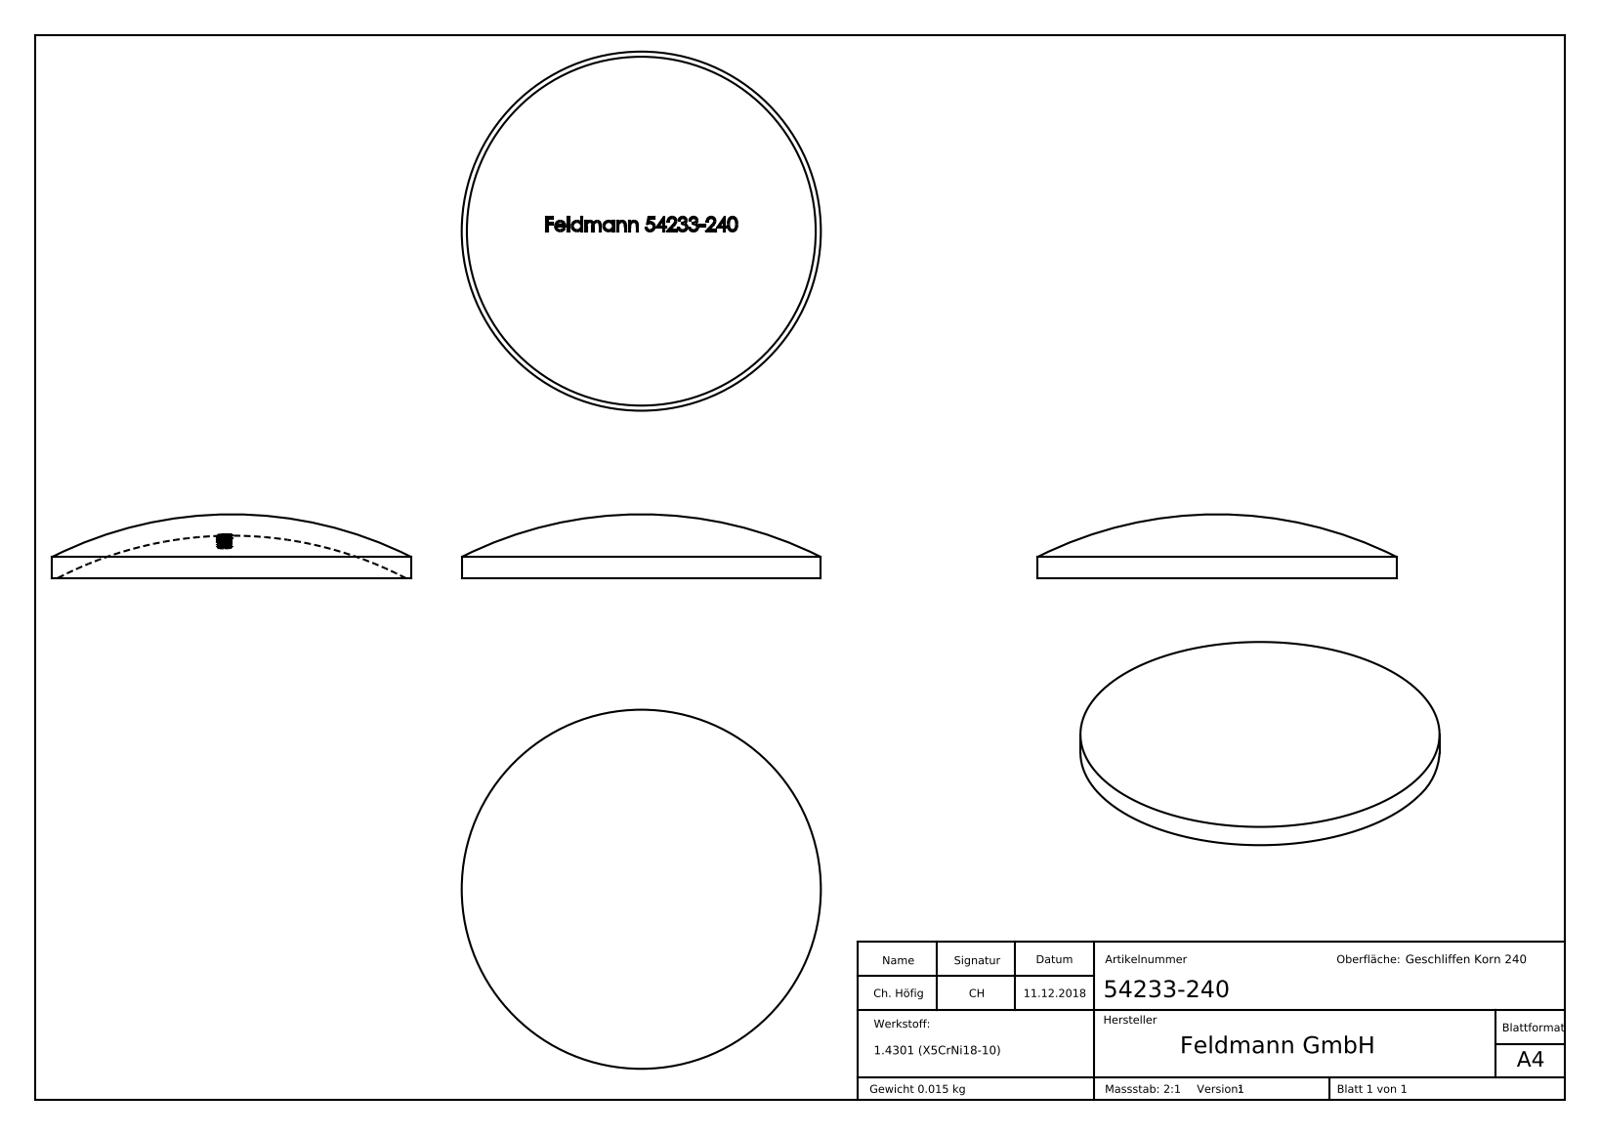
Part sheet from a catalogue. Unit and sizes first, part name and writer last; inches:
Units: inches
Overall size (bounding box): 1.327 × 1.327 × 0.236
Round bosses / shafts (diameter × count): ⌀1.327 ×1
Main face-to-face distances: 0.017, 0.117, 0.015, 0.035, 0.185, 0.052, 0.576, 0.302, 0.431, 0.023
Volume: 0.115 in³ · Surface area: 3.264 in²
Bodies: 1 solid, 256 faces (109 planar, 2 cylindrical, 145 other)
Part name (STEP PRODUCT): 54233-240
STEP written by: SolidWorks 2015 (CONFIG_CONTROL_DESIGN)
